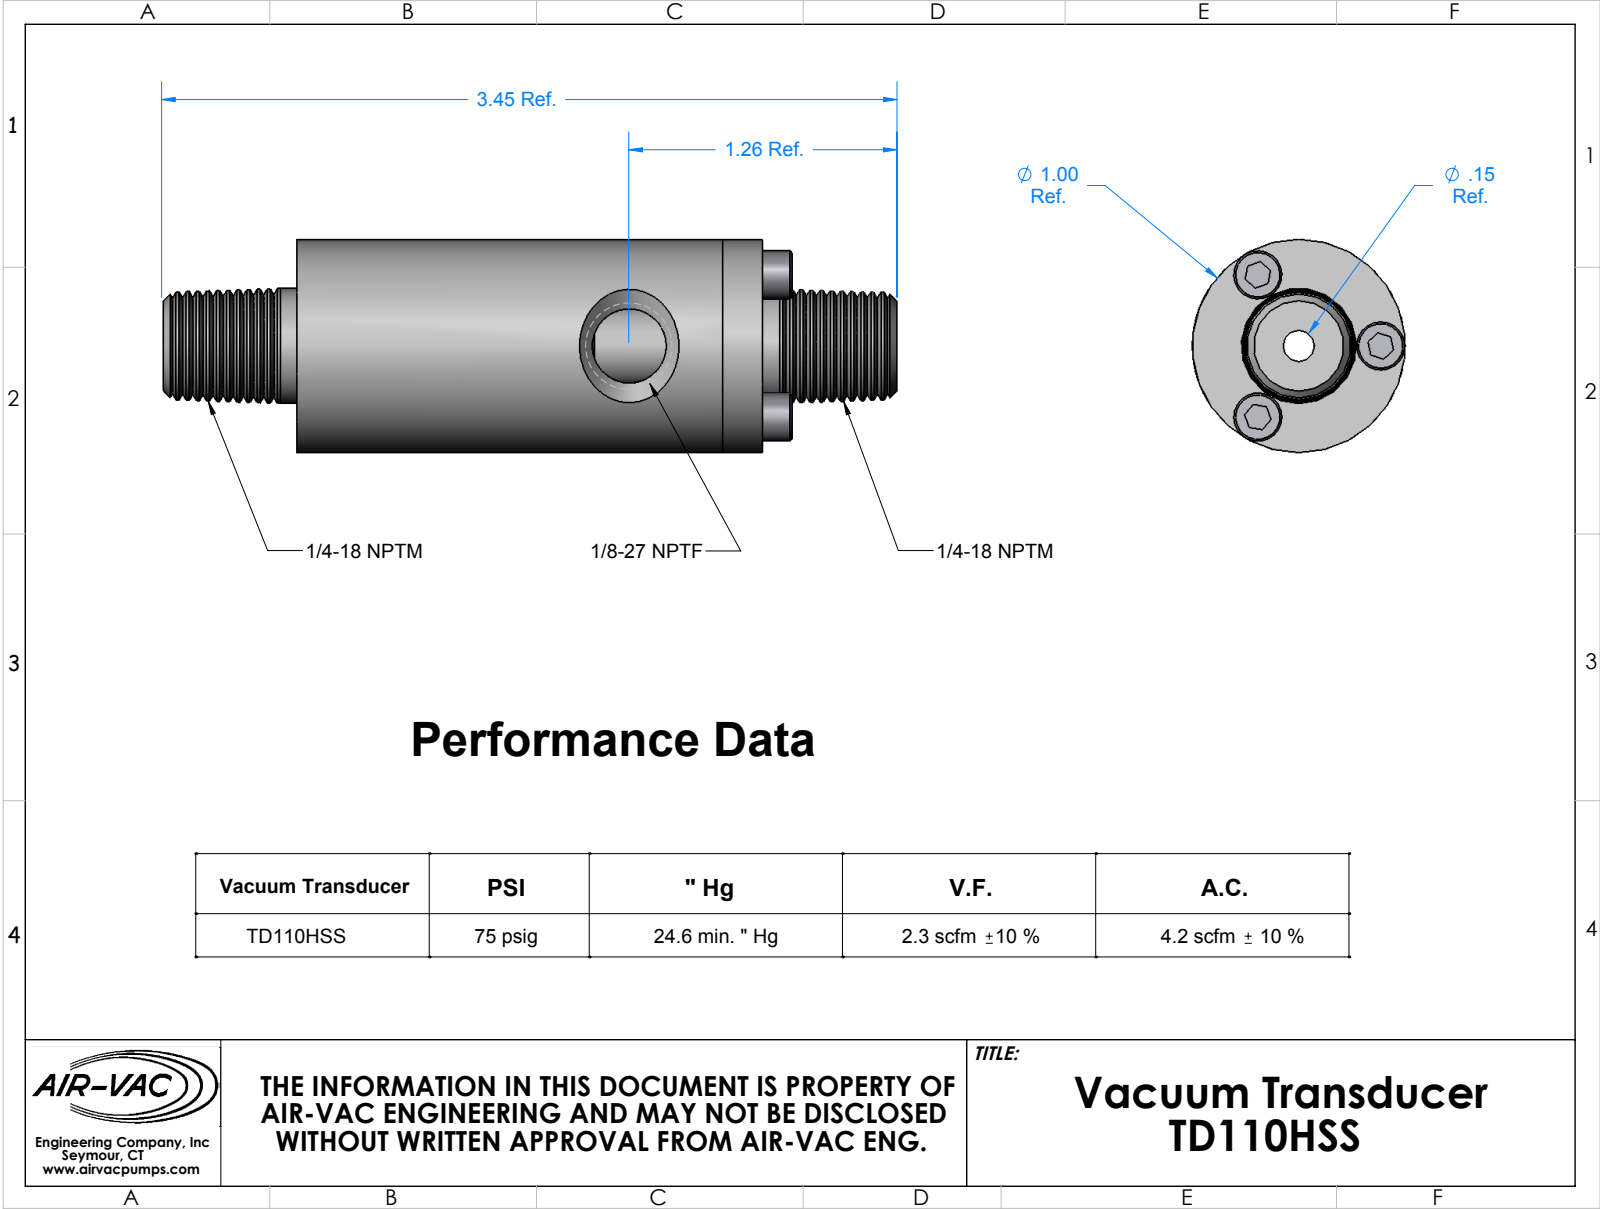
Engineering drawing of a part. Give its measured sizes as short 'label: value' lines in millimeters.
name: TD110HSS; TD110SSB_WEB; TD110HSSG_WEB; SOCKET HEAD CAP SCREW_#6-32 x .375 SS
written by: SolidWorks 2008 (AUTOMOTIVE_DESIGN)
unit: mm
bodies: 5 solids, 243 faces (39 planar, 44 cylindrical, 160 other)
size: 87.6 × 25.4 × 25.4
volume: 30 710 mm³; area: 11 700 mm²
holes: 3× ⌀2.7, 3× ⌀3.6, 1× ⌀3.7, 1× ⌀8.8, 1× ⌀12.7
bosses: 3× ⌀5.7, 3× ⌀3.5, 1× ⌀25.4, 1× ⌀13.7, 1× ⌀12.7, 1× ⌀9.9
face distances: 4.7, 55.5, 50.8, 16, 71.6, 20.8, 87.6, 66.8, 40, 24
hole spacings: 9.8, 16.9
